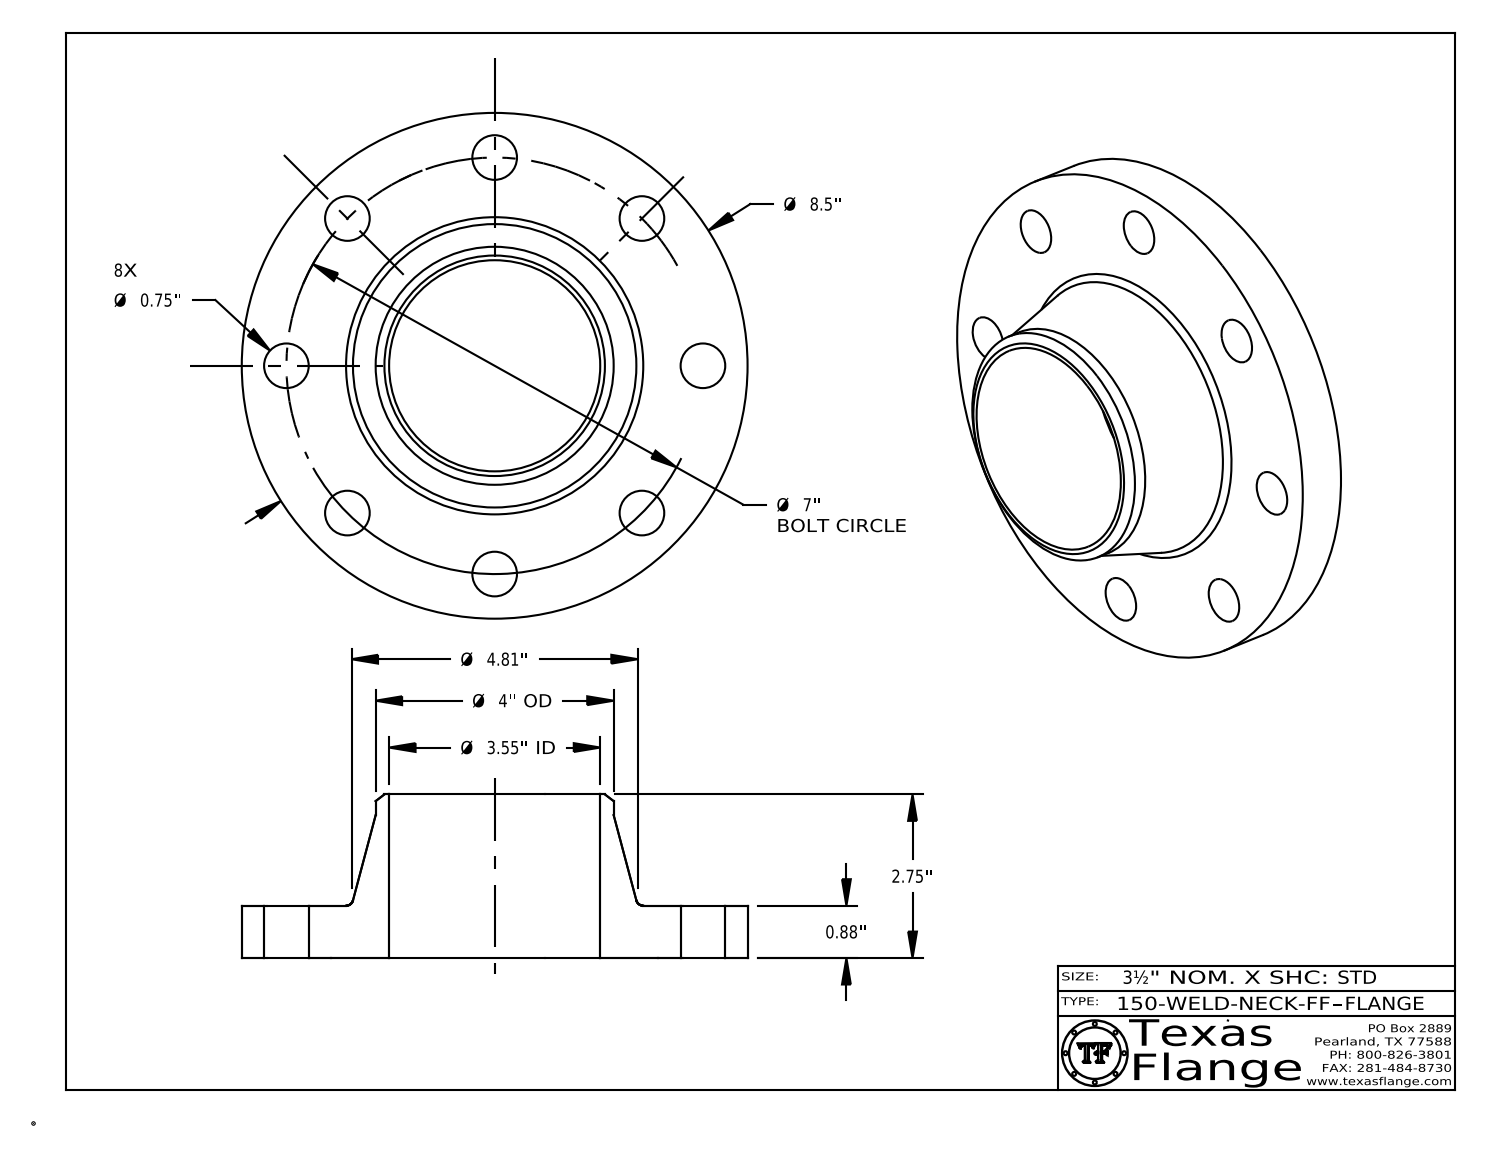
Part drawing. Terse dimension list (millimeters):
name: 150-WELD-NECK-FF
written by: CATIA V5 STEP AP214 (AUTOMOTIVE_DESIGN)
unit: mm
bodies: 1 solid, 417 faces (369 planar, 42 cylindrical, 6 other)
size: 215.9 × 215.9 × 69.9
volume: 773 300 mm³; area: 114 000 mm²
holes: 8× ⌀19.1, 1× ⌀12.6, 1× ⌀90.1
bosses: 8× ⌀0.8, 1× ⌀215.9, 1× ⌀101.6, 1× ⌀9.9
face distances: 22.4, 69.9, 47.5, 22, 0.4, 47.9, 3.8, 3.7, 0.7, 2.4
hole spacings: 88.9, 68, 125.7, 164.3, 34.7, 98.8, 147.8, 174.4
